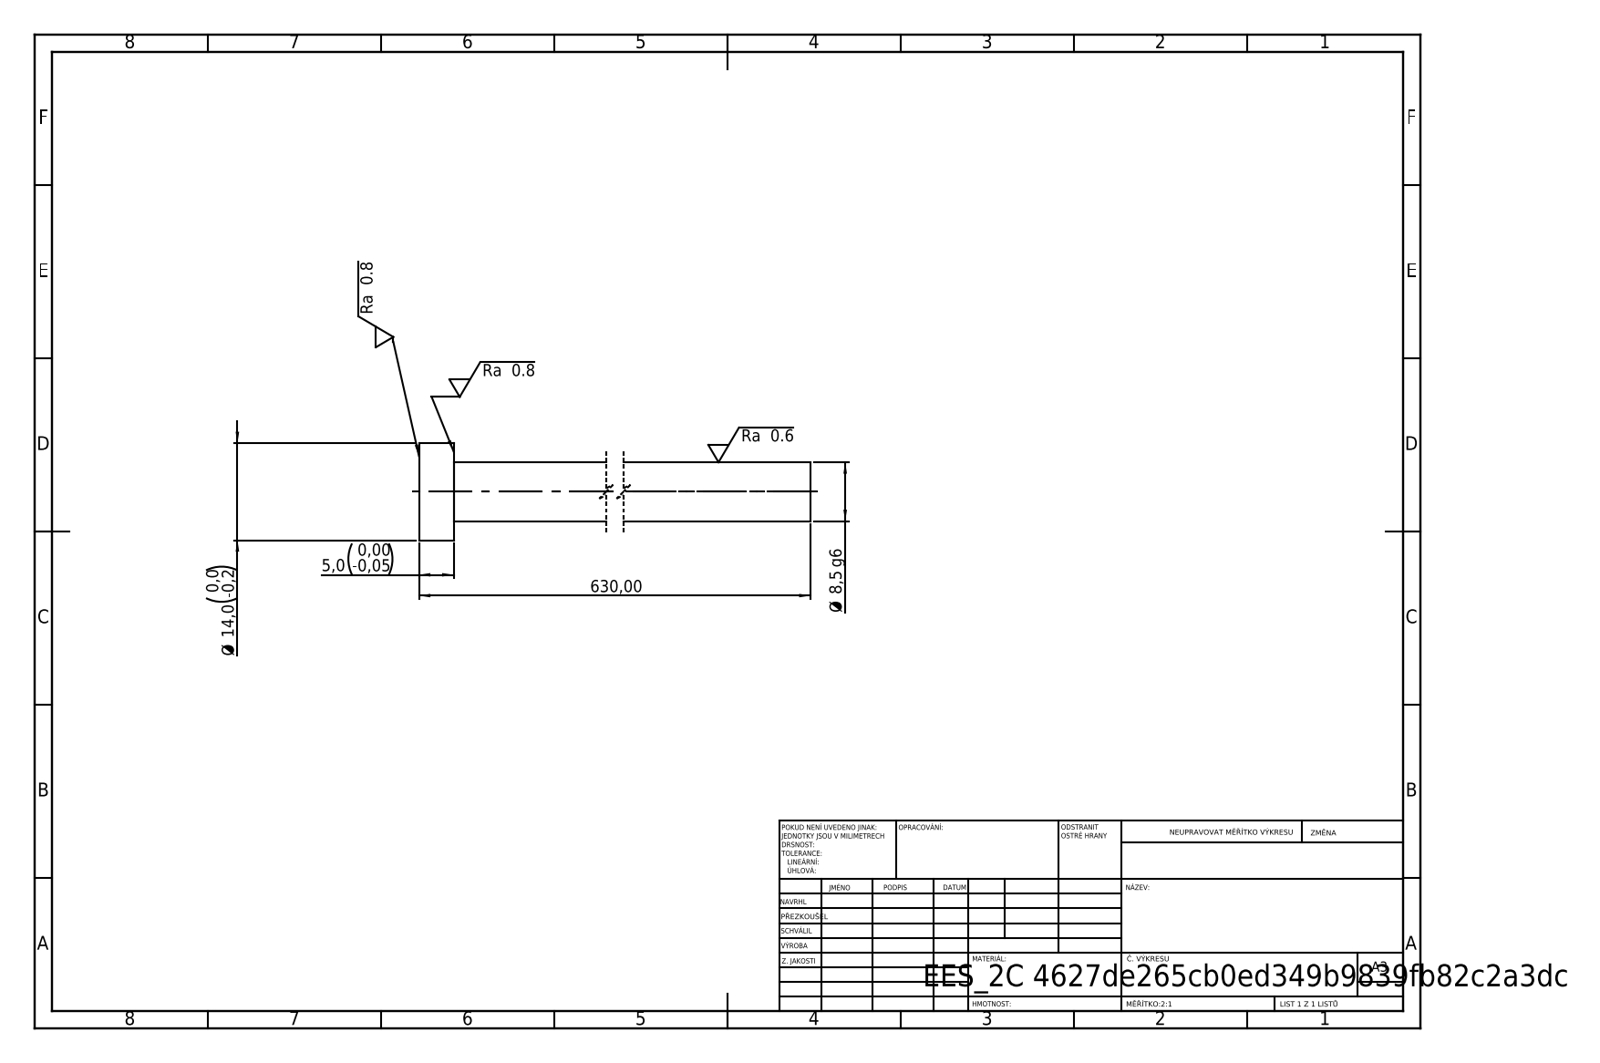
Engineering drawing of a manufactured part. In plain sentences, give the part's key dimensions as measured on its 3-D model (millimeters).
Its 3-D file was written by "SolidWorks 2019 (CONFIG_CONTROL_DESIGN)". It is 1 solid with 7 faces: 3 planar, 4 cylindrical and 0 other. Overall it measures 630 by 14 by 14 millimeters. Its volume is 36 235 cubic millimeters and its surface area 17 218 square millimeters. Round bosses or shafts: 1 of diameter 14, 1 of diameter 8.5. The main face-to-face distances are 5, 630, 625.
